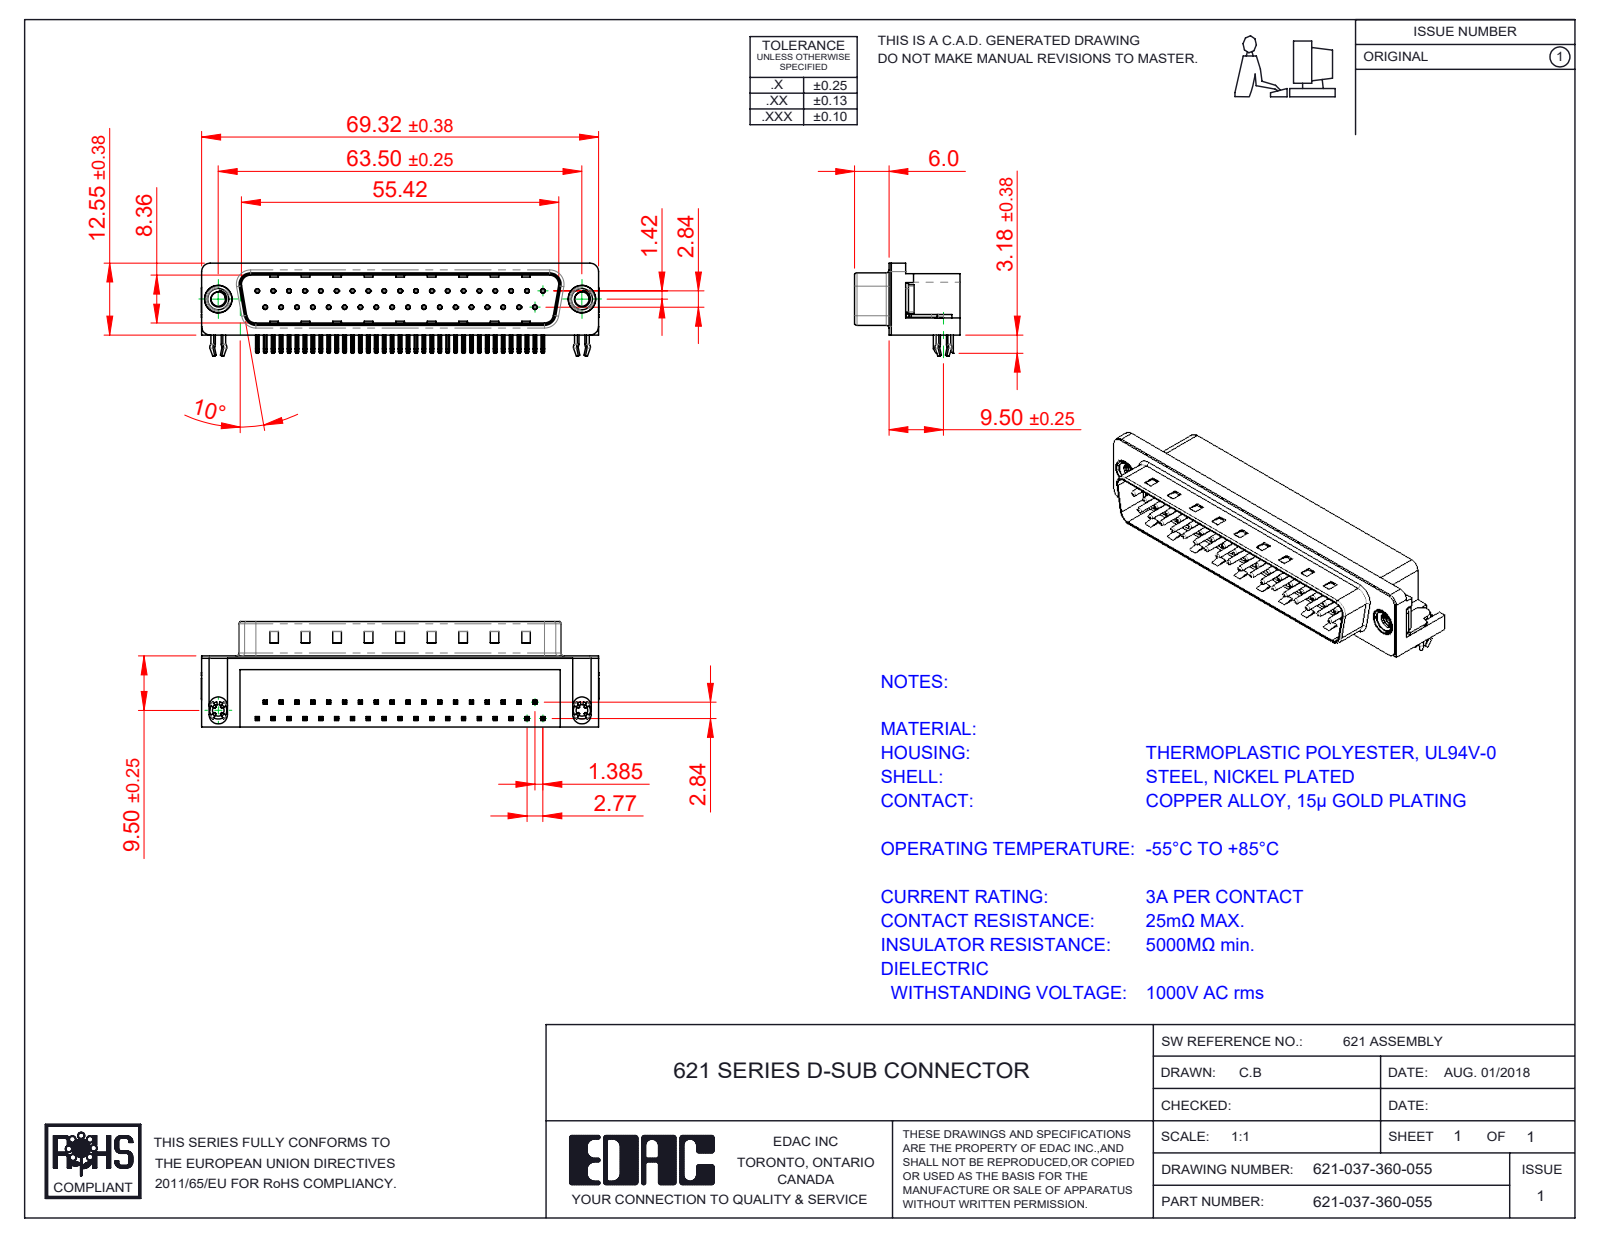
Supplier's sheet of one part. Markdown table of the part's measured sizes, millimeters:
| quantity | value |
| --- | --- |
| part name | 621 Housing_37 Socket; 621 Contact Bottom; 621 M3 Threaded Rivet; 621 4-40 Threaded Board Mount (+3 more) |
| STEP written by | SolidWorks 2016 (CONFIG_CONTROL_DESIGN) |
| units | millimeters |
| bodies | 43 solids, 3229 faces (2013 planar, 931 cylindrical, 285 other) |
| overall size | 69.4 × 18.4 × 15.73 |
| volume | 8 627 mm³ |
| surface area | 10 177 mm² |
| round holes (diameter × count) | 0.35 × 37, 0.8 × 37, 2.26 × 2, 2.5 × 2, 4 × 2, 4.8 × 2, 5 × 2 |
| round bosses / shafts (diameter × count) | 0.75 × 37, 4.9 × 2, 4.75 × 2, 3.9 × 2, 3.26 × 2 |
| partial cylindrical surfaces (radius × count) | 0.25 × 156, 0.12 × 74, 1 × 16, 0.5 × 9, 1.6 × 8, 1.5 × 7, 0.9 × 4, 2 × 4 |
| main face-to-face distances | 0.4, 12, 10.35, 8.76, 2.1, 1.7, 10.46, 10.86, 9, 12.4 |
| hole center spacings | 3.16, 2.77, 5.54, 8.31, 11.08, 13.85, 19.39, 22.16 |
